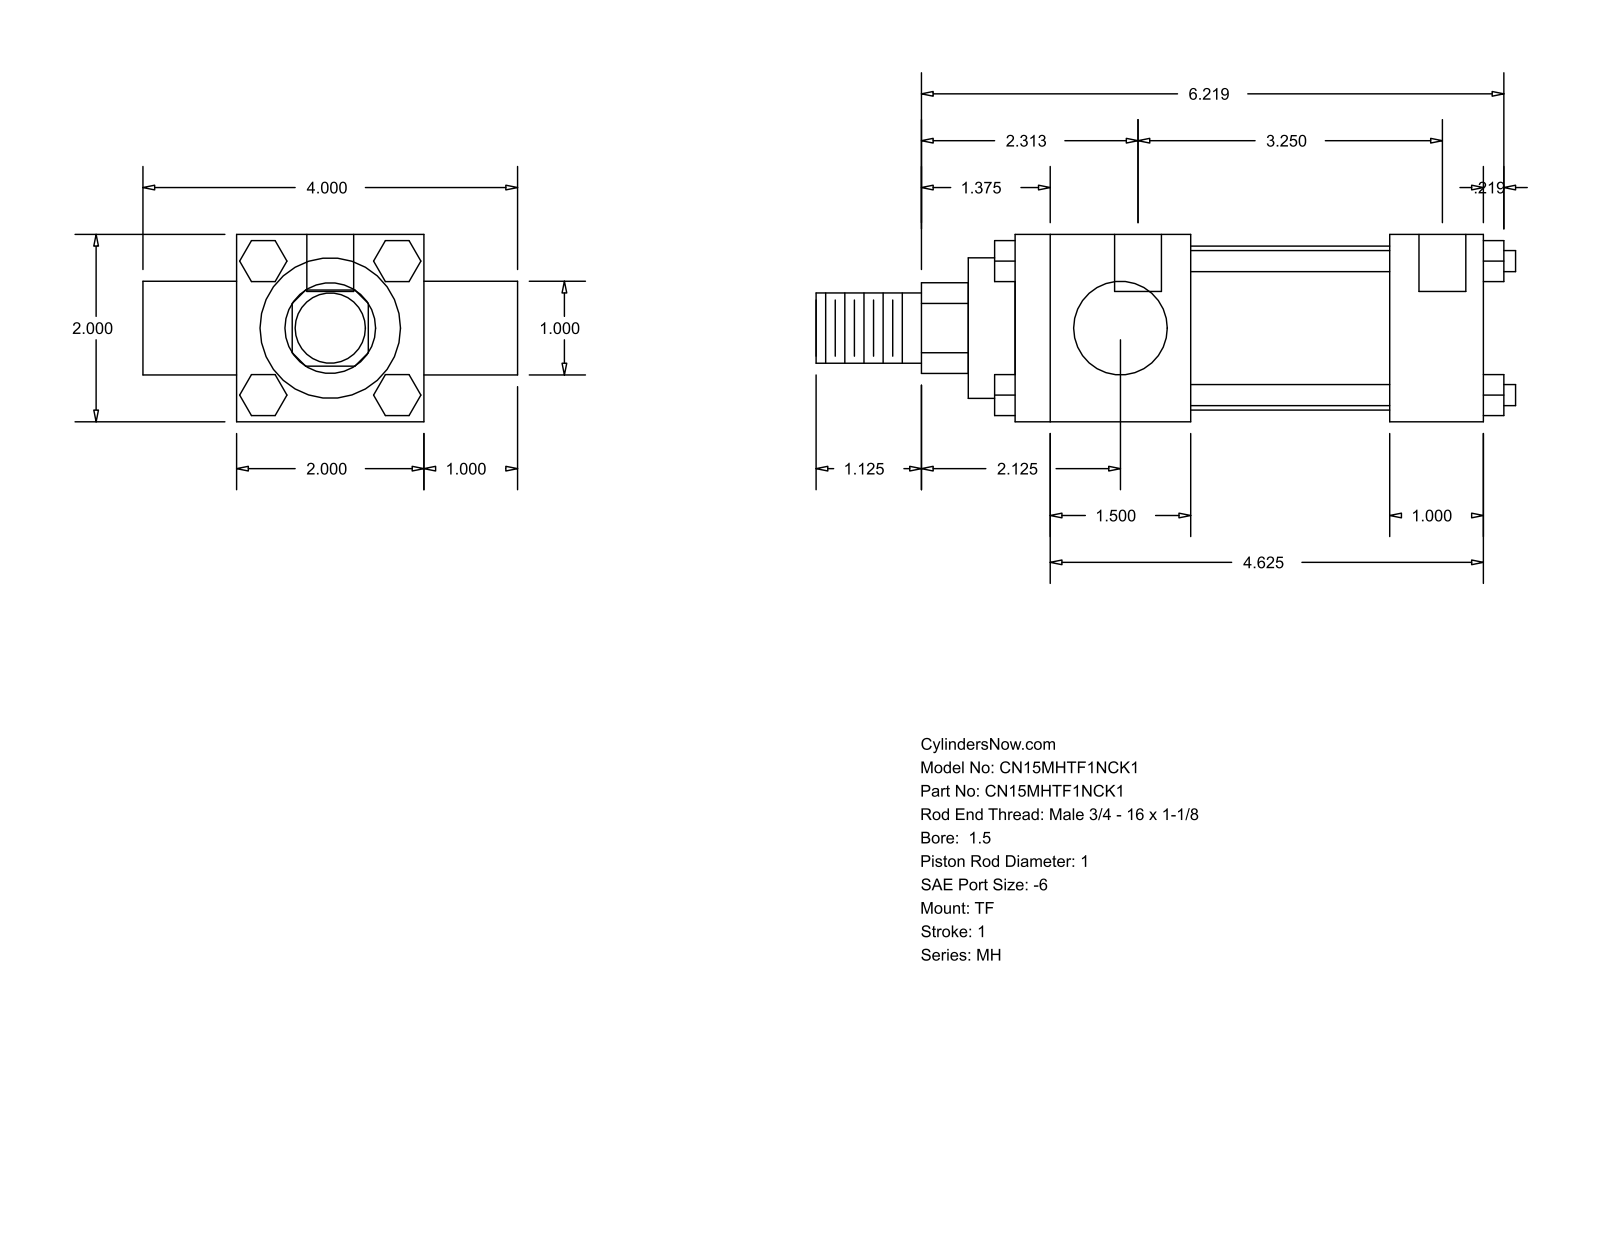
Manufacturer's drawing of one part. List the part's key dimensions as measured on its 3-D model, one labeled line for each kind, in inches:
Part name (STEP PRODUCT): MH_TF__0150_1
STEP written by: GSSL Pune (CONFIG_CONTROL_DESIGN)
Units: inches
Bodies: 0 solids, 120 faces (92 planar, 28 cylindrical, 0 other)
Overall size (bounding box): 7.469 × 4 × 2
Round holes (diameter × count): ⌀0.219 ×3, ⌀0.5 ×2
Round bosses / shafts (diameter × count): ⌀0.225 ×4, ⌀1 ×2, ⌀1.75 ×1, ⌀1.5 ×1, ⌀0.75 ×1
Partial cylindrical surfaces — rounded edges, fillets, slot ends (radius × count): R0.484 ×1
Main face-to-face distances: 2, 1, 4, 2.125, 5, 3, 1.875, 3.125, 0.5, 0.219
Hole centre spacings: 0.125, 3.25, 3.375
